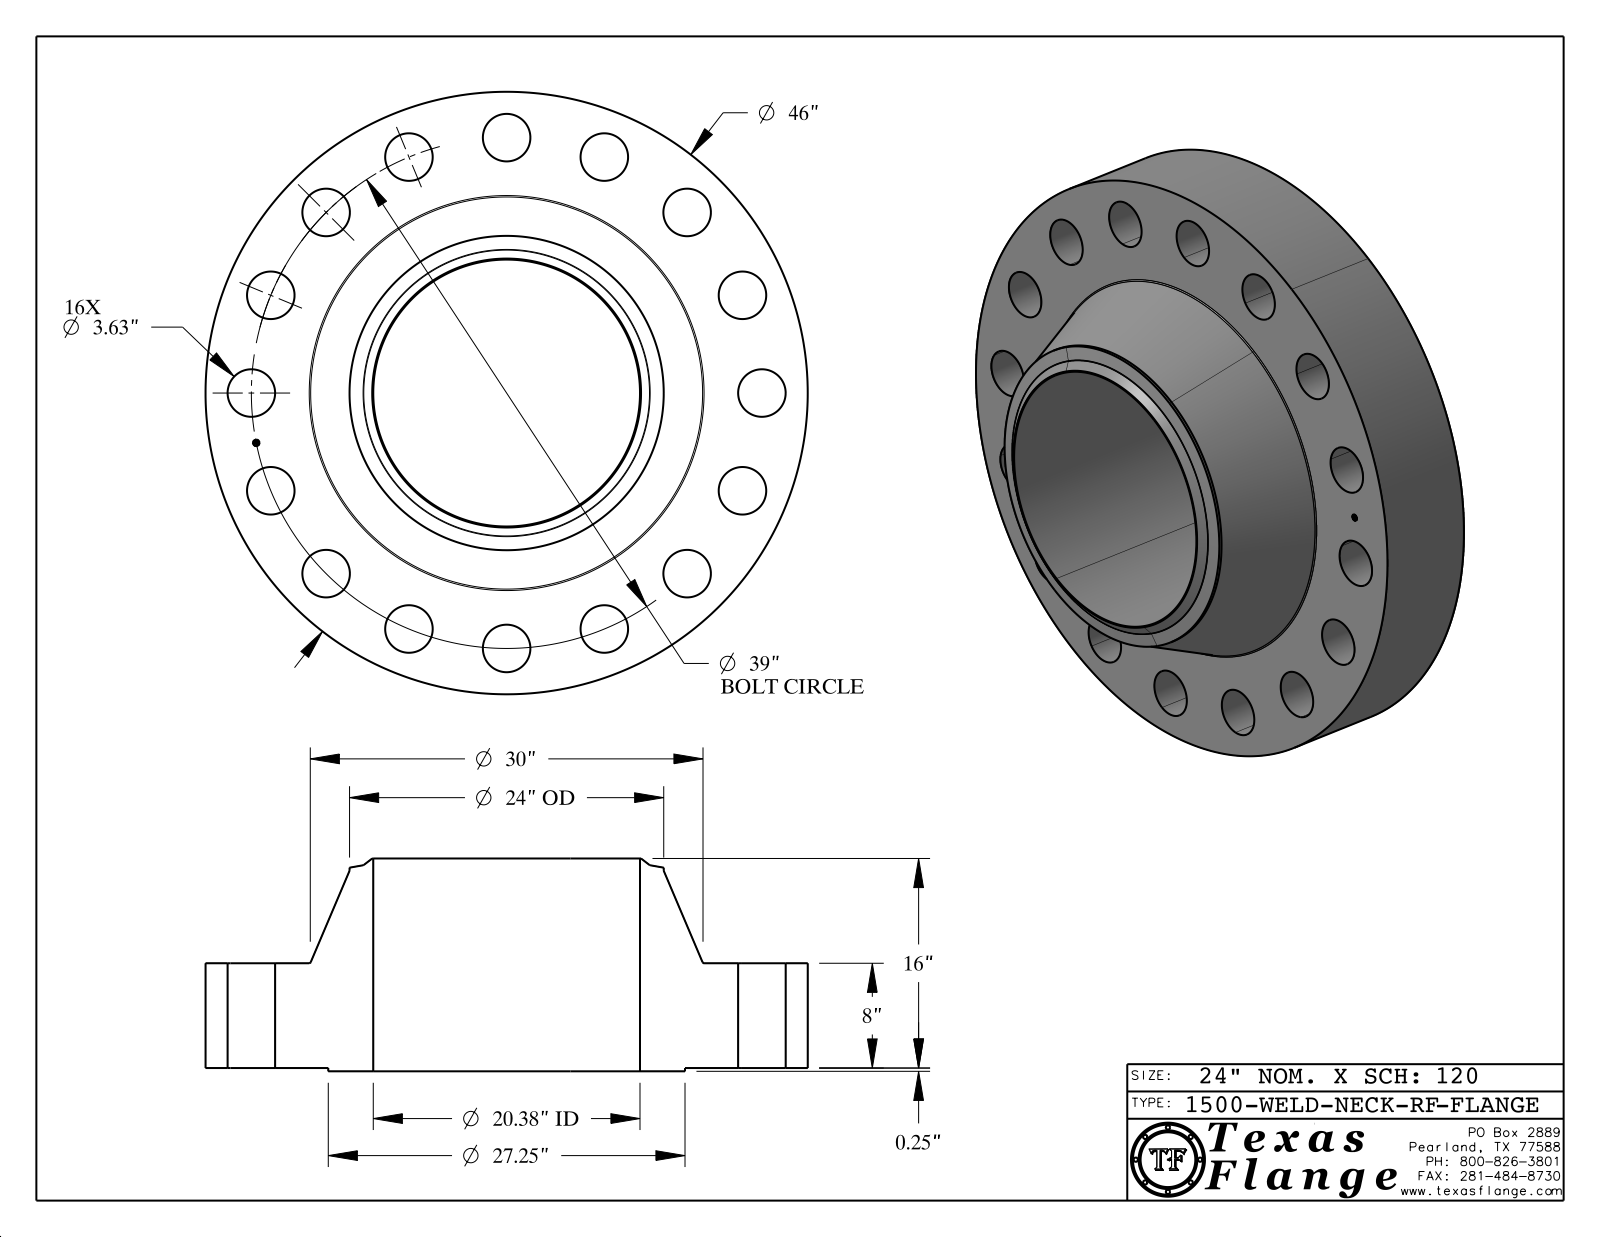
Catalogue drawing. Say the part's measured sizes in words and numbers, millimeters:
The part is named "1500-WELD-NECK-RF". Its 3-D file was written by "CATIA V5 STEP AP214 (AUTOMOTIVE_DESIGN)". It is 1 solid with 439 faces: 369 planar, 60 cylindrical and 10 other. Overall it measures 1168.4 by 1168.4 by 412.8 millimeters. Its volume is 184 300 000 cubic millimeters and its surface area 4 157 000 square millimeters. Round holes: 16 of diameter 92.2, 1 of diameter 12.6, 1 of diameter 517.6. Round bosses or shafts: 8 of diameter 0.8, 1 of diameter 1168.4, 1 of diameter 692.2, 1 of diameter 609.6, 1 of diameter 9.9. The main face-to-face distances are 203.2, 6.4, 209.6, 412.8, 406.4, 209.2, 202.8, 0.4, 203.6, 3.8. The hole center spacings are 495.3, 550.3, 700.5, 971.6, 379.1, 915.2, 193.2, 193.3.
